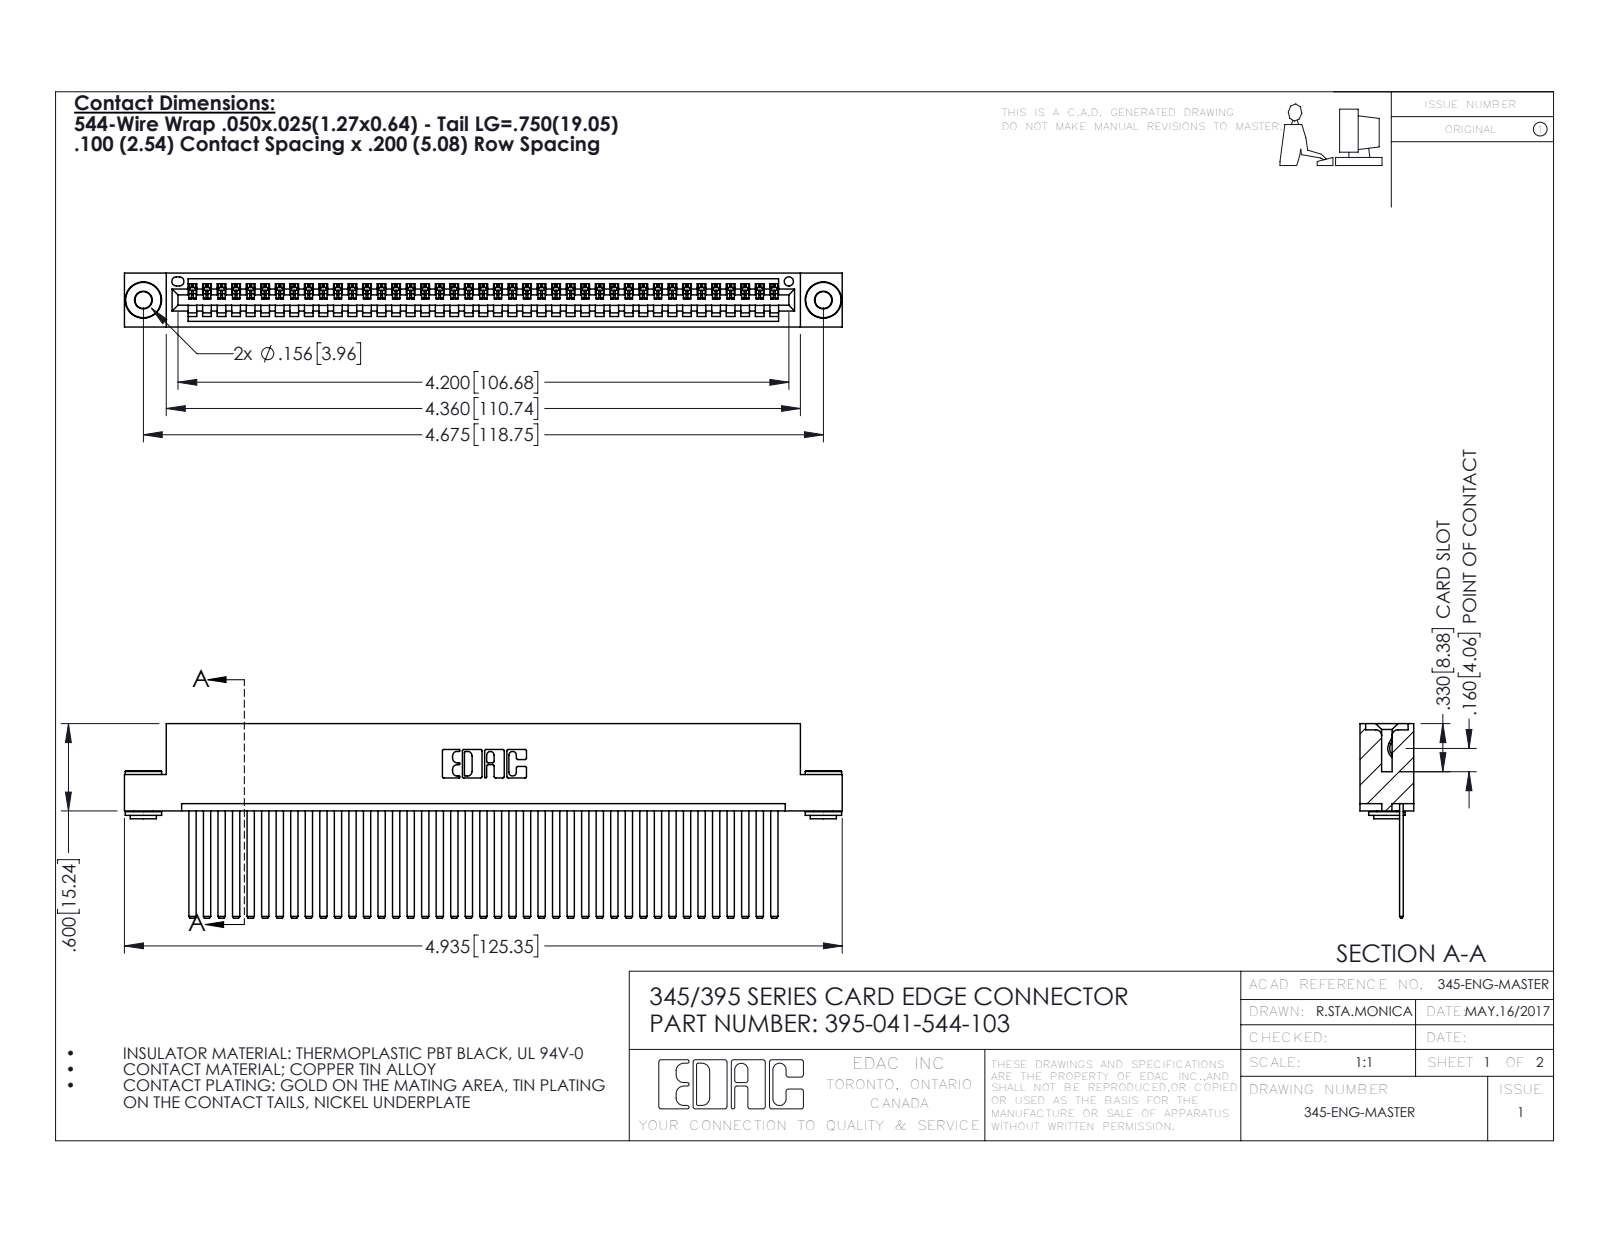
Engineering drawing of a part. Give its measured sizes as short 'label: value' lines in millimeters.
name: 345 Part_Flush Mounting Lugs - 0.156 Dia-TH; 345-292-001_345-293-144; 395-041-544-103; 345-250-002_345-250-002-102
written by: SolidWorks 2016 (CONFIG_CONTROL_DESIGN)
unit: mm
bodies: 44 solids, 2296 faces (1566 planar, 722 cylindrical, 8 other)
size: 125.3 × 34 × 9.4
volume: 12 400 mm³; area: 18 100 mm²
holes: 2× ⌀2.9, 2× ⌀4, 1× ⌀1.6
bosses: 2× ⌀6.4, 2× ⌀4.6, 2× ⌀3.5
rounds: 82× R0.2, 22× R0.3, 6× R0.2, 6× R0.8, 3× R0.7, 2× R0.8, 2× R1, 1× R0.4
face distances: 1.8, 7.6, 0.6, 2.5, 6.9, 9.4, 5.1, 5.7, 3.8, 1.8
hole spacings: 6.9, 112.8, 118.7
